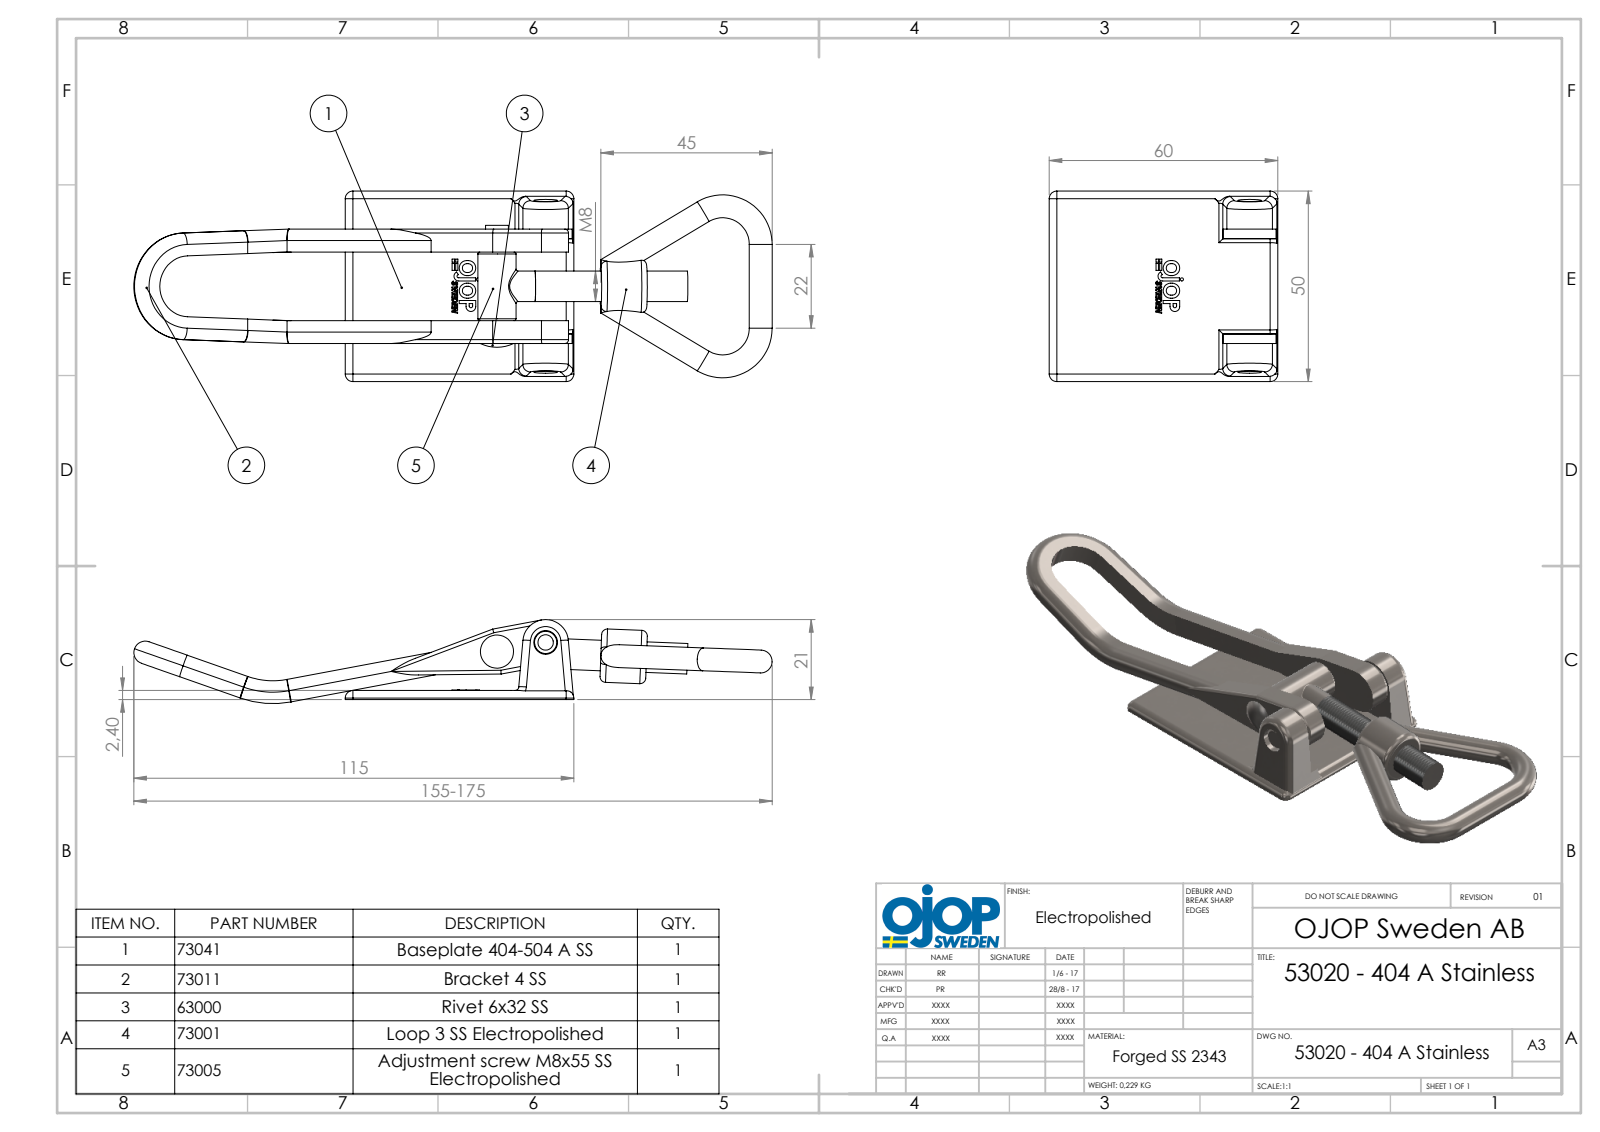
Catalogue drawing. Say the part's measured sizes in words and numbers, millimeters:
The part is named "53020 - 404 A RF; Bygel 4; Ring 3; 404-504 A RF (+2 more)". Its 3-D file was written by "SolidWorks 2015 (AUTOMOTIVE_DESIGN)". It is 5 solids with 195 faces: 57 planar, 80 cylindrical and 58 other. Overall it measures 167.77 by 50 by 21 millimeters. Its volume is 28 075 cubic millimeters and its surface area 19 777 square millimeters. Round holes: 2 of diameter 6.2, 1 of diameter 3, 1 of diameter 6.3, 1 of diameter 8.1. Round bosses or shafts: 4 of diameter 6, 1 of diameter 10, 1 of diameter 8.01, 1 of diameter 8, 1 of diameter 5.85. Partial cylindrical surfaces (rounded edges, fillets, slot ends): 18 of radius 3, 8 of radius 2, 4 of radius 1, 4 of radius 6.99, 2 of radius 1.5, 1 of radius 6, 1 of radius 8, 1 of radius 20. The main face-to-face distances are 2.4, 6, 18, 24, 30, 12, 8.96, 2.96, 3.04, 9.04. The hole center spacings are 13.
